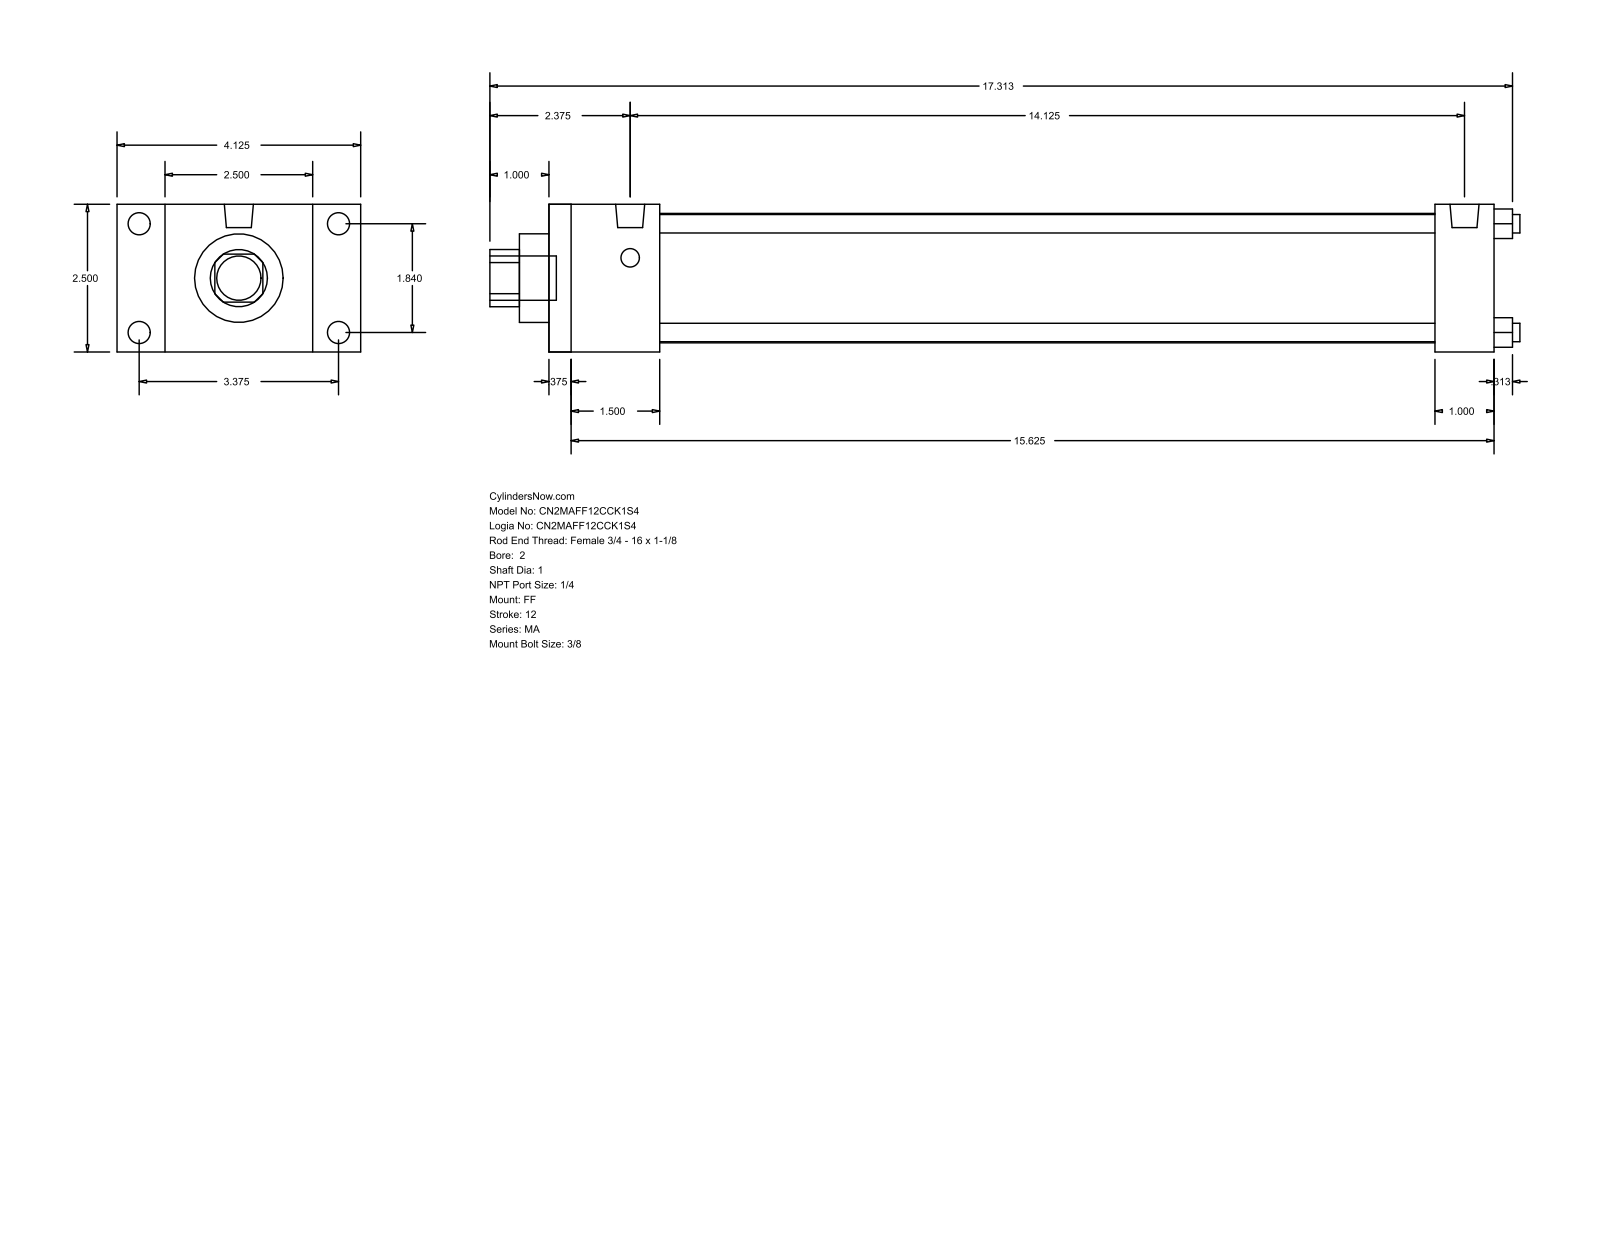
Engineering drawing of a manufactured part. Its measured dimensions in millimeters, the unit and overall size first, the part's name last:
Units: millimetres
Overall size (bounding box): 442.91 × 104.78 × 63.5
Round holes (diameter × count): ⌀7.94 ×4, ⌀25.4 ×1, ⌀38.1 ×1, ⌀55.63 ×1
Round bosses / shafts (diameter × count): ⌀9.53 ×4, ⌀7.94 ×4, ⌀12.49 ×2, ⌀19.05 ×1
Partial cylindrical surfaces — rounded edges, fillets, slot ends (radius × count): R12.29 ×1
Main face-to-face distances: 63.5, 406.4, 9.52, 396.88, 25.4, 20.64, 12.7, 47.63, 381, 38.11
Hole centre spacings: 33.05, 46.74, 66.1
Bodies: 0 solids, 92 faces (64 planar, 28 cylindrical, 0 other)
Part name (STEP PRODUCT): MA_FF__0200_1
STEP written by: GSSL Pune (CONFIG_CONTROL_DESIGN)
